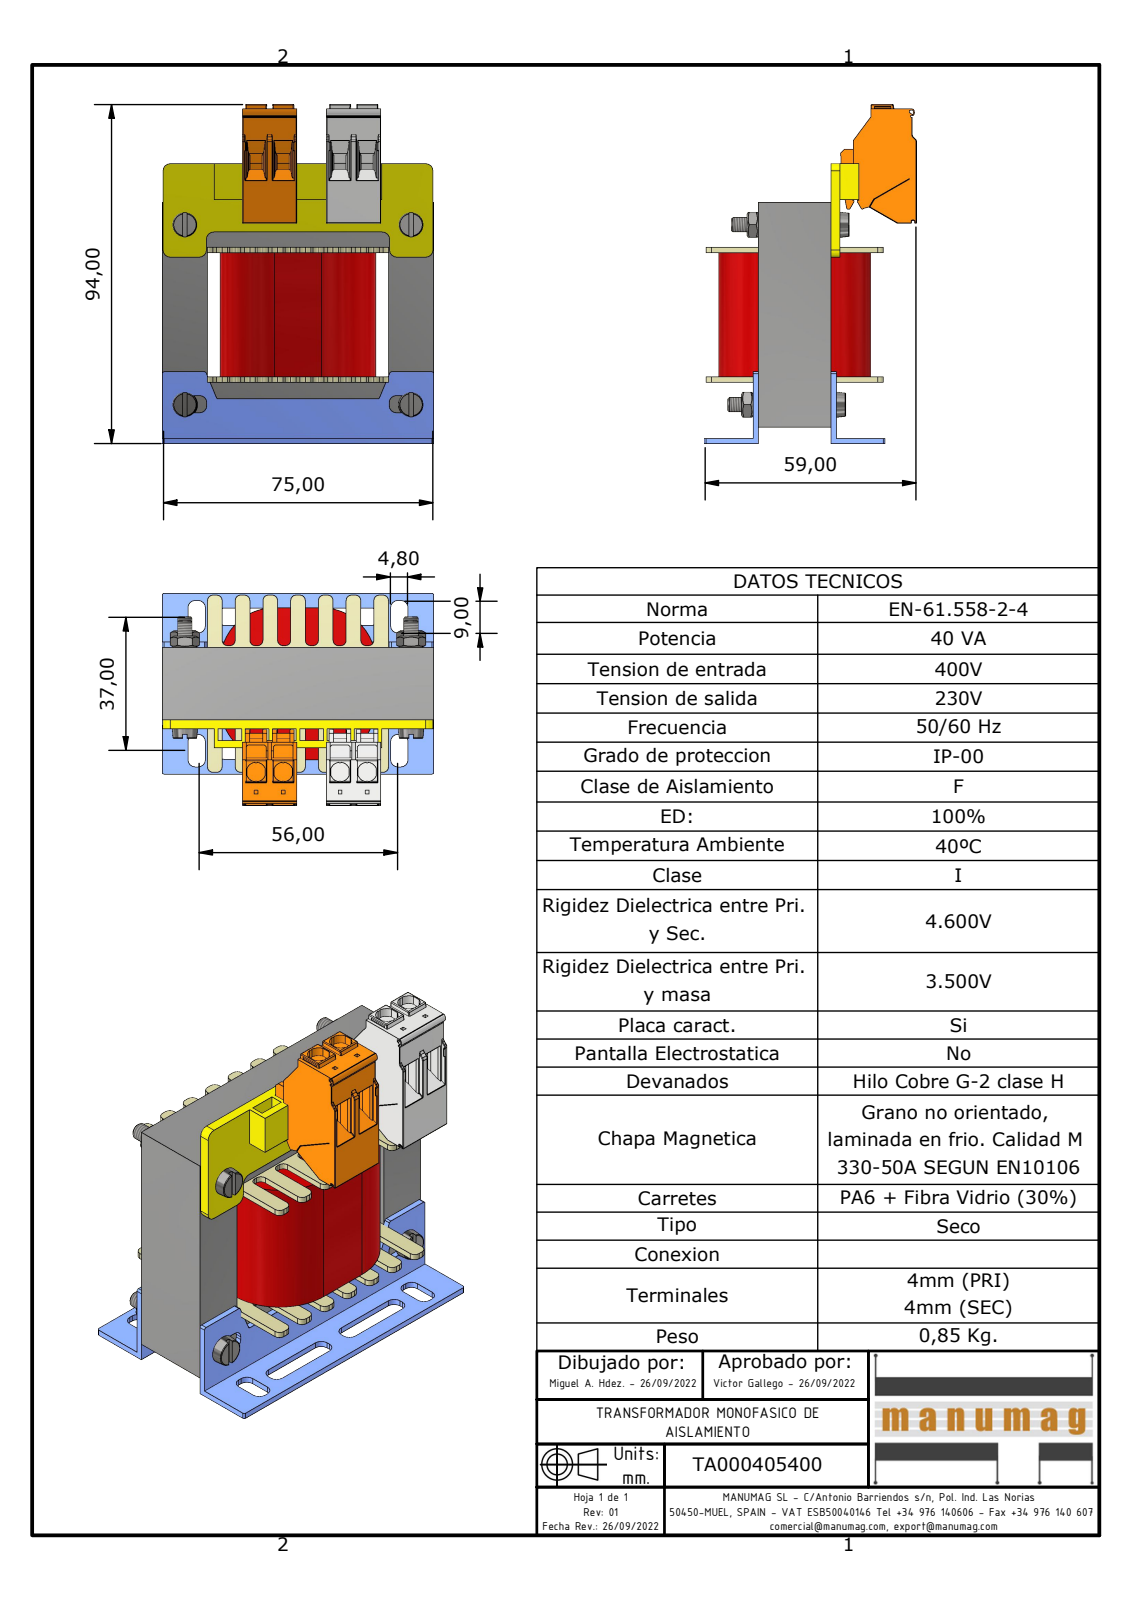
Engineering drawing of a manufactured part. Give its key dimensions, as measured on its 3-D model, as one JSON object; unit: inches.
{"part_name": "TA000405400; EI75 x 62,5 - 20 (RC25); AF25DIN; DIN 934 - M4 x 0,7 (+5 more)", "step_written_by": "Autodesk Inventor 2023 (AUTOMOTIVE_DESIGN)", "units": "inches", "bodies": {"solids": 15, "faces": 3810, "planar": 3032, "cylindrical": 556, "other": 222}, "overall_size": [3.715, 2.953, 2.311], "volume_in3": 8.425, "surface_area_in2": 92.75, "round_holes": [[0.128, 4], [0.177, 4], [0.157, 2]], "round_bosses_or_shafts": [[0.143, 4], [0.157, 2]], "partial_cylinders_radius": [[0.006, 160], [0.059, 52], [0.008, 48], [0.079, 48], [0.02, 22], [0.012, 7], [0.039, 4], [0.106, 4]], "face_to_face_distances": [0.492, 1.969, 0.787, 0.059, 0.984, 1.476, 2.461, 0.673, 2.091, 0.551], "hole_center_spacings": [1.969, 2.461, 3.151]}
